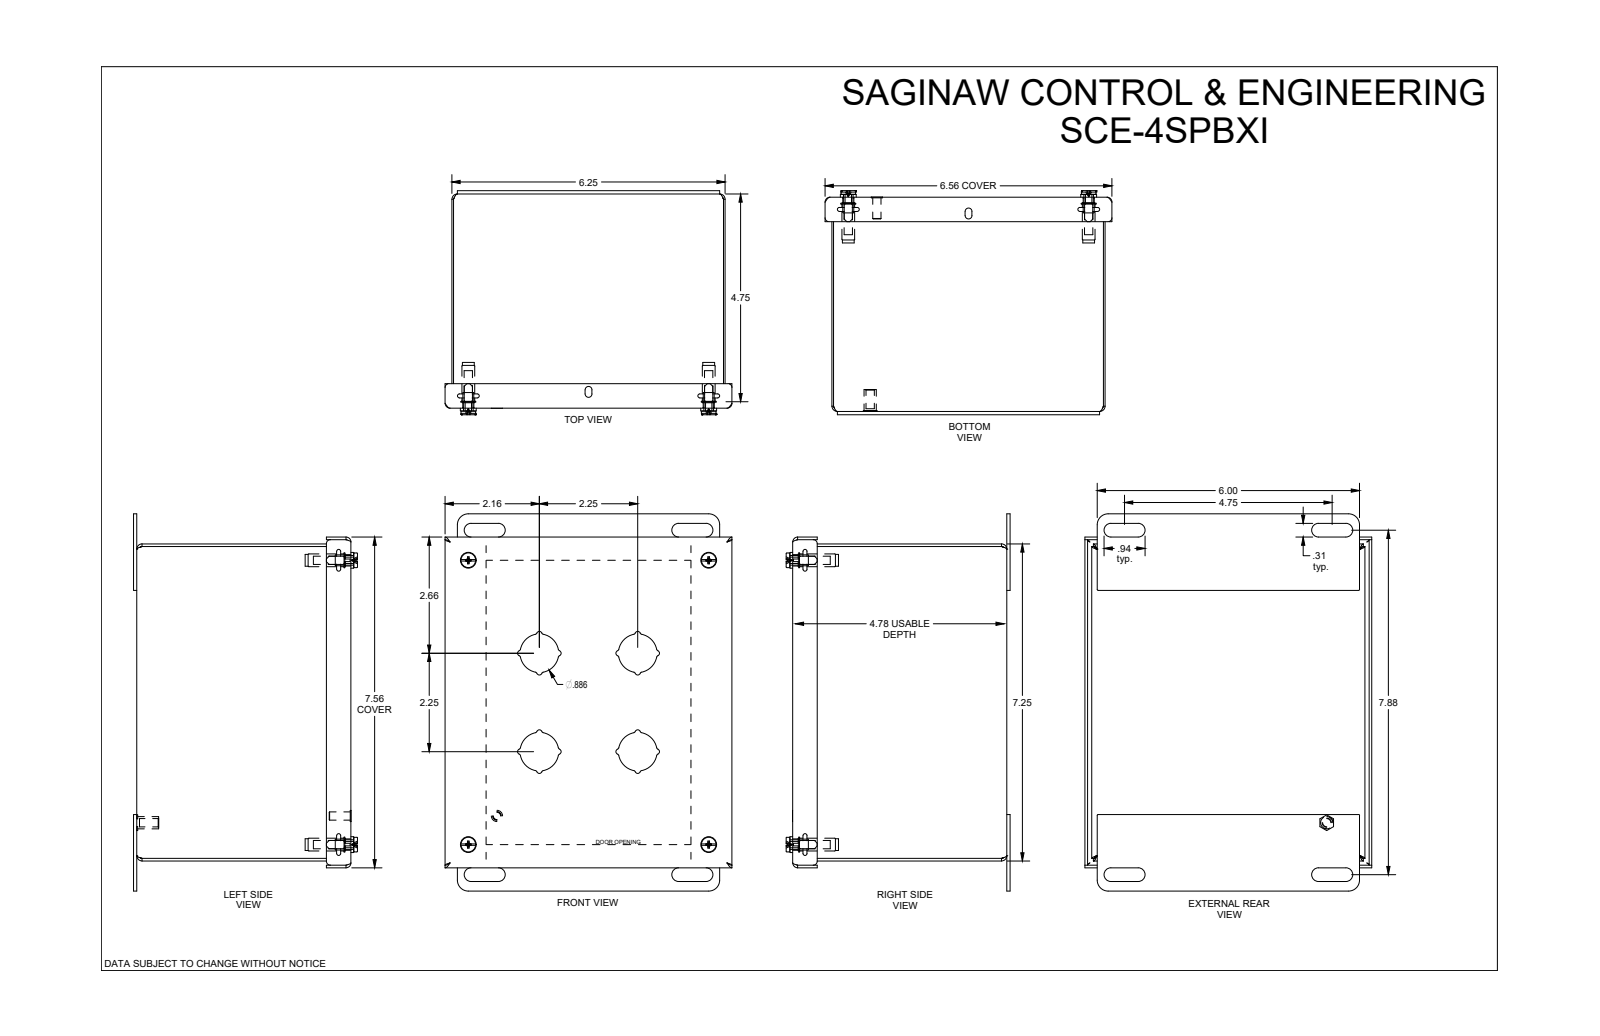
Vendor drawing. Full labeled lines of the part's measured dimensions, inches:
Part name (STEP PRODUCT): SCE-4SPBXI
STEP written by: SolidWorks 2021 (AUTOMOTIVE_DESIGN)
Units: inches
Bodies: 3 solids, 482 faces (154 planar, 244 cylindrical, 84 other)
Overall size (bounding box): 8.625 × 6.563 × 5.036
Volume: 16.56 in³ · Surface area: 523.5 in²
Round holes (diameter × count): ⌀0.19 ×5, ⌀0.22 ×4, ⌀0.25 ×4, ⌀0.266 ×4, ⌀0.317 ×4
Round bosses / shafts (diameter × count): ⌀0.362 ×4, ⌀0.34 ×4, ⌀0.292 ×4, ⌀0.27 ×4, ⌀0.26 ×4, ⌀0.28 ×1, ⌀0.256 ×1, ⌀0.188 ×1
Partial cylindrical surfaces — rounded edges, fillets, slot ends (radius × count): R0.04 ×32, R0.06 ×20, R0.062 ×16, R0.015 ×8, R0.115 ×8, R0.156 ×8, R0.245 ×8, R0.02 ×4
Main face-to-face distances: 0.06, 4.838, 6.19, 7.19, 4.778, 4.898, 6.25, 6.13, 7.25, 7.13
Hole centre spacings: 8.515, 5.5, 5.5, 6.5, 6.5, 8.514, 0.7, 0.707
